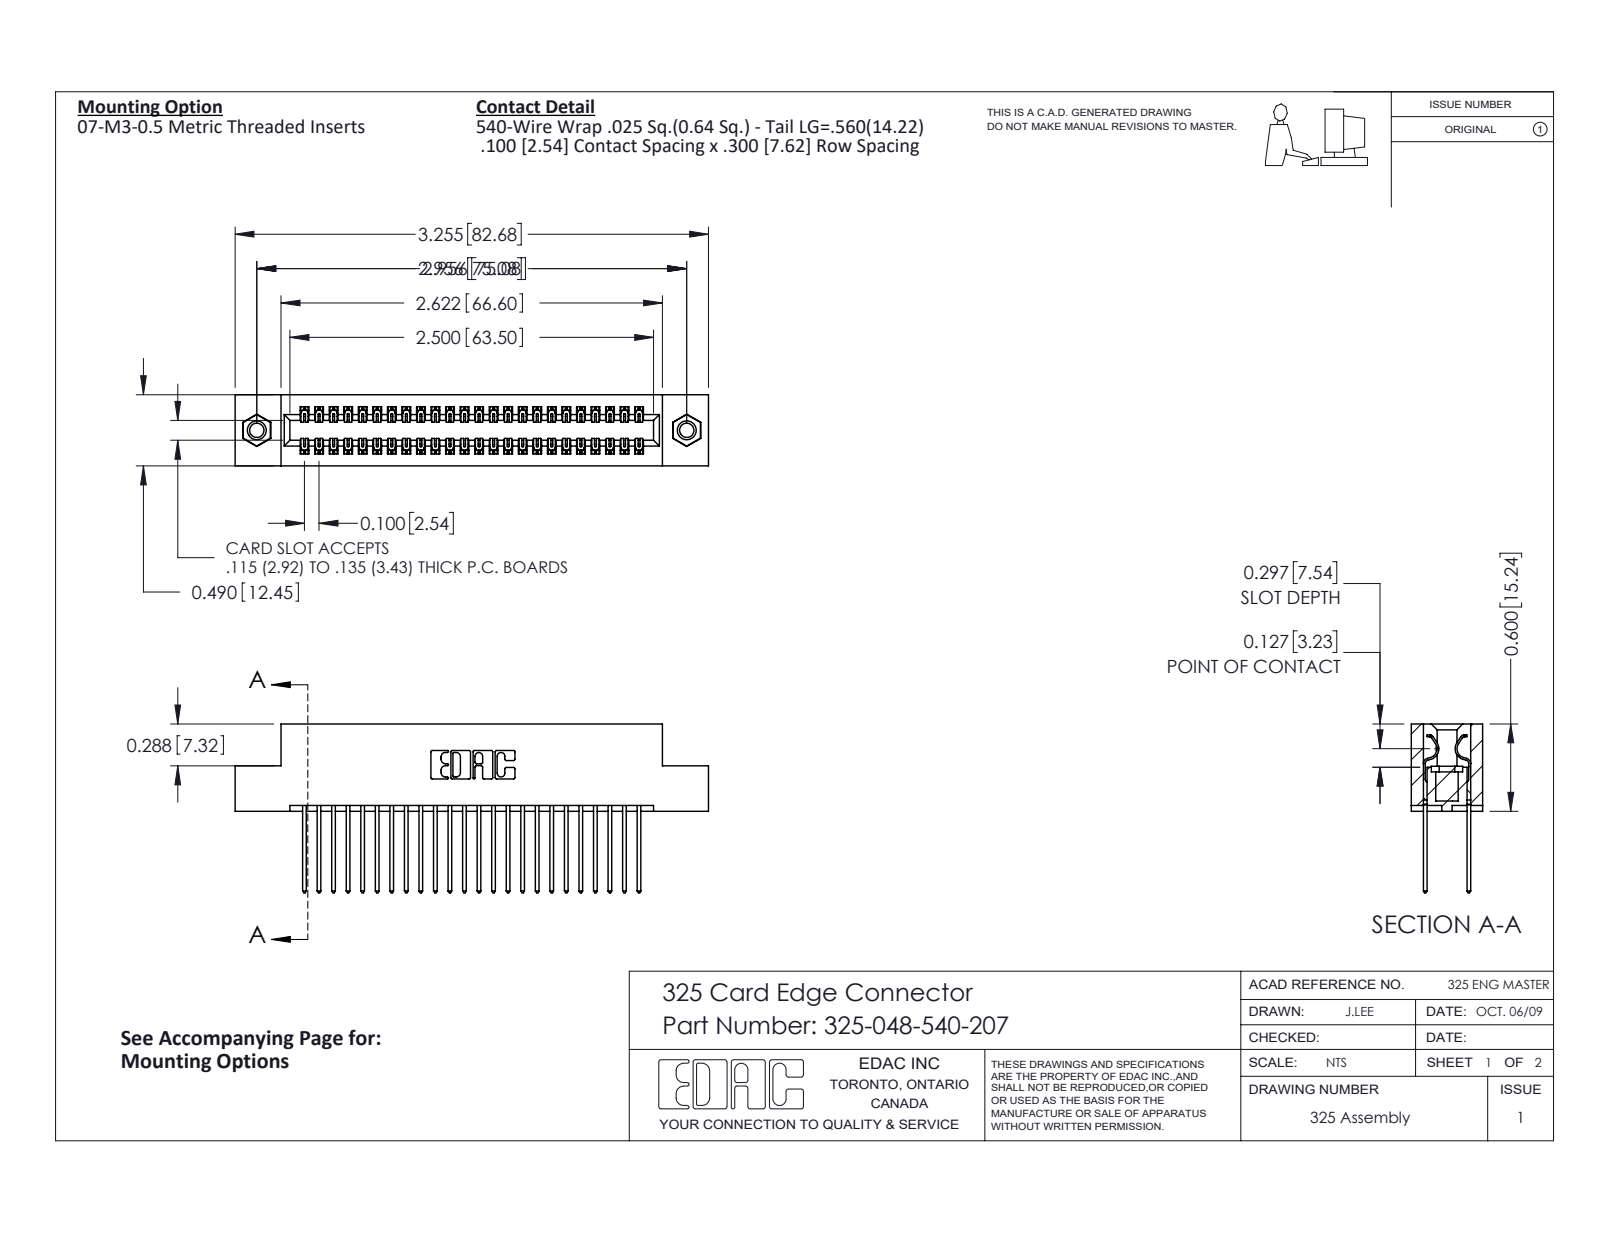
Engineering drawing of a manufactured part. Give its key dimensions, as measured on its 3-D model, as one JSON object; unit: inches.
{"part_name": "345-250-001_345-250-005-103; 325 Part_TI; 325-048-540-207; 325-292-001_325-293-140", "step_written_by": "SolidWorks 2016 (CONFIG_CONTROL_DESIGN)", "units": "inches", "bodies": {"solids": 51, "faces": 2670, "planar": 1830, "cylindrical": 824, "other": 16}, "overall_size": [3.255, 1.16, 0.49], "volume_in3": 0.652, "surface_area_in2": 20.76, "round_holes": [[0.098, 2], [0.125, 2], [0.16, 2]], "round_bosses_or_shafts": [[0.155, 2]], "partial_cylinders_radius": [[0.006, 72], [0.01, 48], [0.01, 22], [0.007, 6], [0.031, 6], [0.026, 3], [0.014, 2], [0.022, 2]], "face_to_face_distances": [0.083, 0.407, 0.3, 0.107, 0.383, 0.025, 0.49, 0.325, 0.275, 0.04], "hole_center_spacings": [2.956]}
